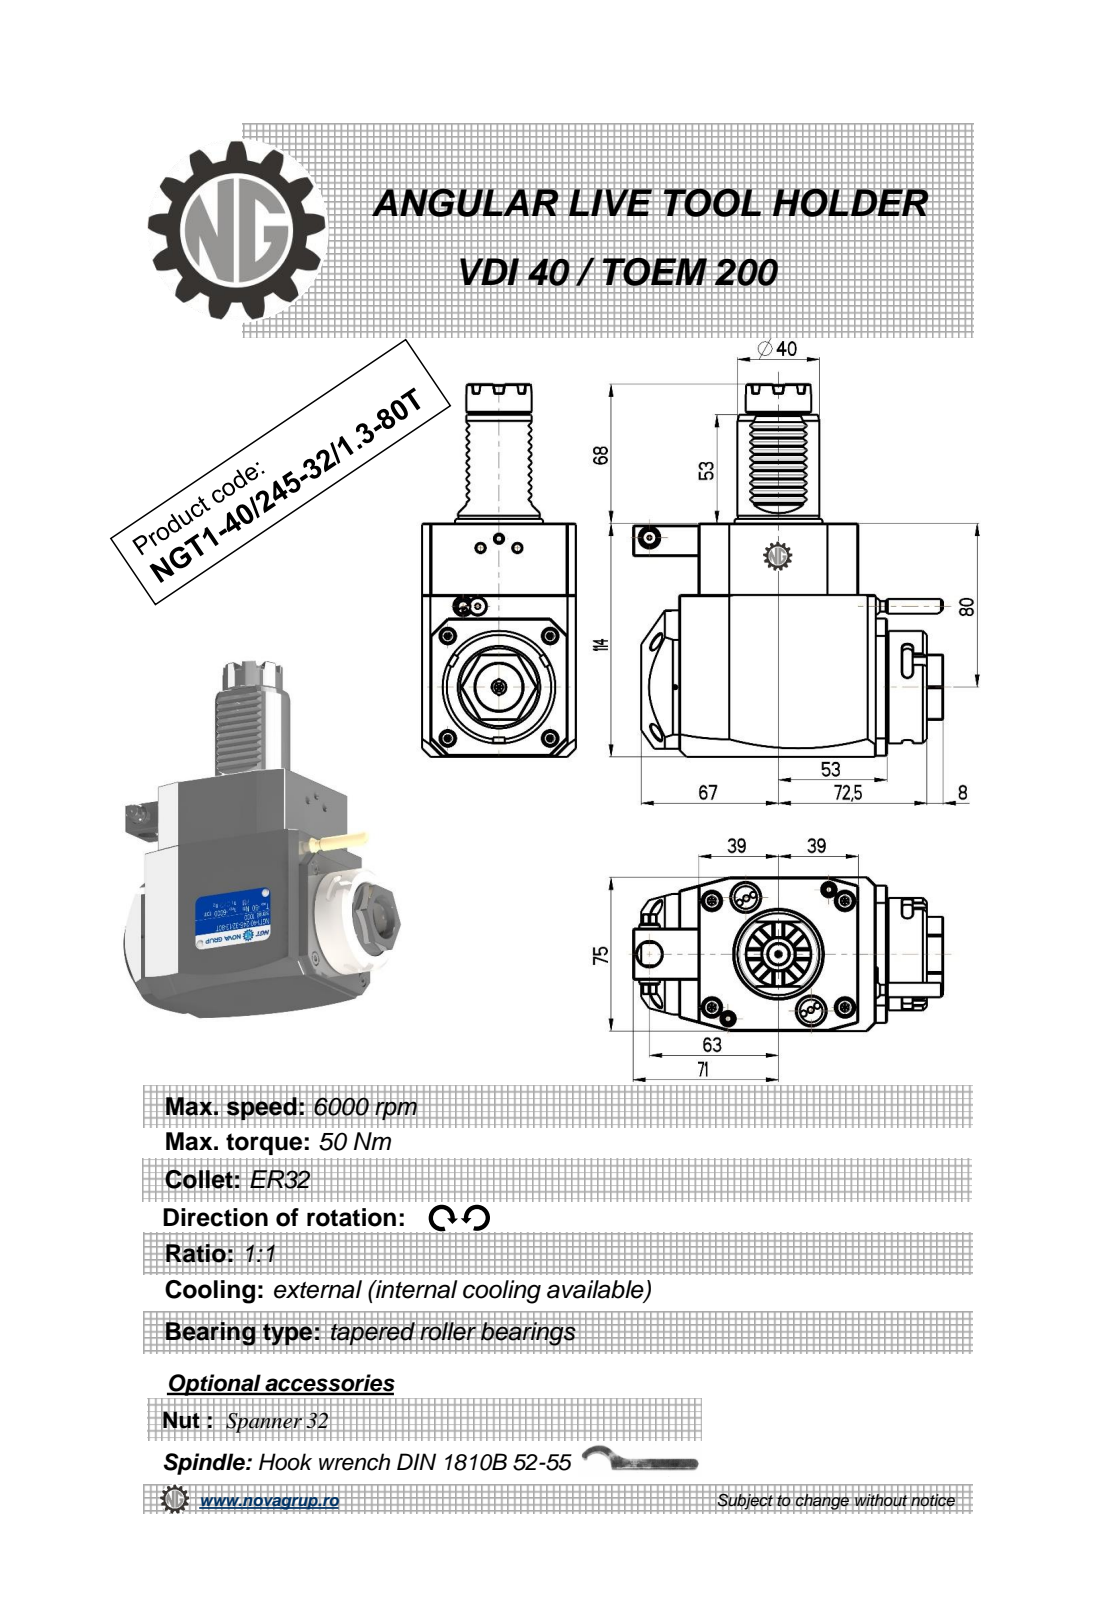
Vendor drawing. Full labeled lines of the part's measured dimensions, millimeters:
Part name (STEP PRODUCT): NGT1_40_245_32_1_3_80T
STEP written by: PRO/ENGINEER BY PARAMETRIC TECHNOLOGY CORPORATION, 2010280 (CONFIG_CONTROL_DESIGN)
Units: millimetres
Bodies: 1 solid, 474 faces (263 planar, 93 cylindrical, 118 other)
Overall size (bounding box): 182 × 151.5 × 75
Volume: 957 908 mm³ · Surface area: 73 190 mm²
Round holes (diameter × count): ⌀2 ×1, ⌀2.5 ×1, ⌀3 ×1, ⌀4.5 ×1, ⌀9.5 ×1, ⌀12 ×1, ⌀23 ×1
Round bosses / shafts (diameter × count): ⌀8 ×2, ⌀55 ×1, ⌀48 ×1, ⌀40 ×1, ⌀32 ×1, ⌀17.2 ×1, ⌀10 ×1, ⌀7 ×1
Partial cylindrical surfaces — rounded edges, fillets, slot ends (radius × count): R0.3 ×20, R2.5 ×6, R180 ×2, R3.85 ×1, R4.25 ×1, R24.5 ×1, R37.5 ×1
Main face-to-face distances: 75, 114, 14, 78, 92, 25, 111.5, 33.5, 19.5, 4
Hole centre spacings: 37.35, 43.2, 72.5
